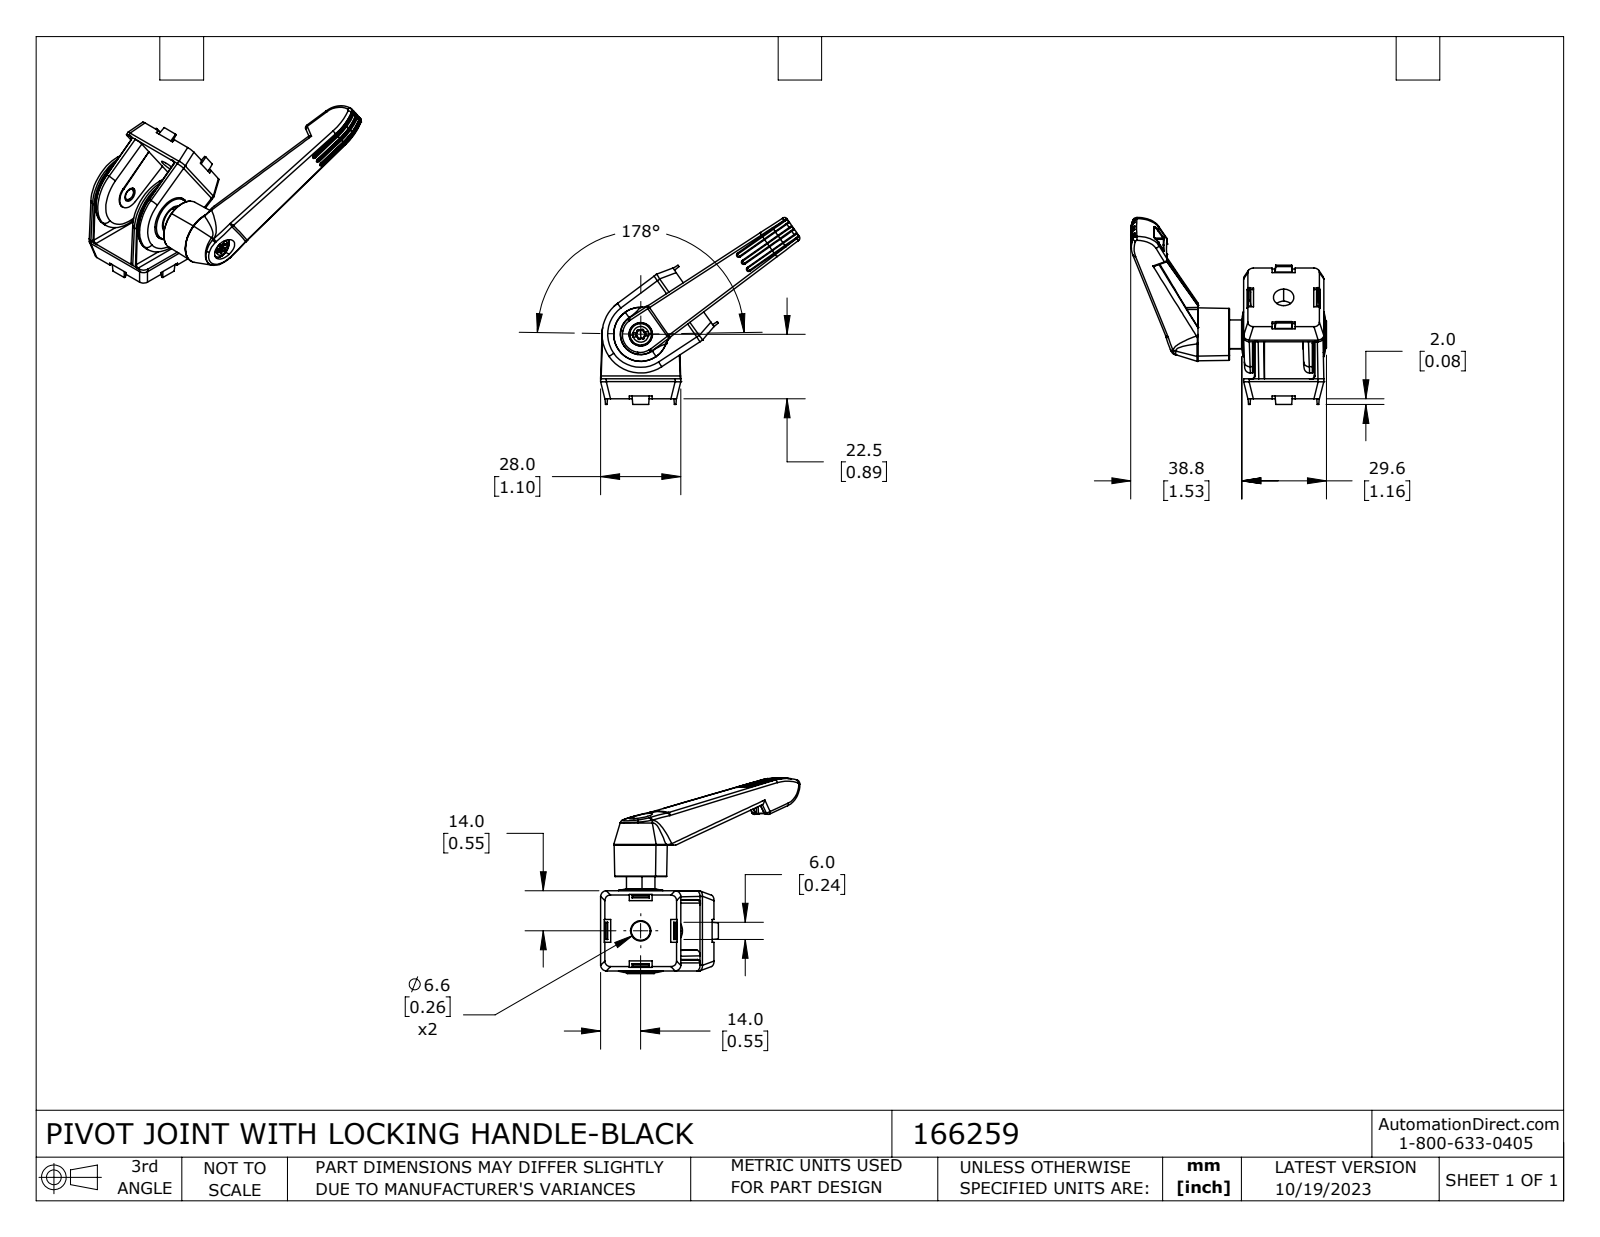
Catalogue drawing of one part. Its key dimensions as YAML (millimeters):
part_name: "166259"
step_written_by: "SolidWorks 2023 (CONFIG_CONTROL_DESIGN)"
units: millimeters
bodies: {solids: 8, faces: 640, planar: 213, cylindrical: 142, other: 285}
overall_size: [69.6, 68.34, 65.31]
volume: 26043
surface_area: 19027
round_holes:
  - {diameter: 2.5, count: 4}
  - {diameter: 4.2, count: 1}
  - {diameter: 5.2, count: 1}
  - {diameter: 7.5, count: 1}
  - {diameter: 8.2, count: 1}
  - {diameter: 22, count: 1}
round_bosses_or_shafts:
  - {diameter: 27, count: 1}
  - {diameter: 15.5, count: 1}
  - {diameter: 14, count: 1}
  - {diameter: 11.2, count: 1}
  - {diameter: 10, count: 1}
  - {diameter: 9.4, count: 1}
  - {diameter: 9, count: 1}
  - {diameter: 8, count: 1}
partial_cylinders:
  - {radius: 2, count: 24}
  - {radius: 0.5, count: 13}
  - {radius: 0.2, count: 10}
  - {radius: 0.4, count: 6}
  - {radius: 0.3, count: 4}
  - {radius: 1, count: 4}
  - {radius: 0.1, count: 3}
face_to_face_distances: [0.5, 7, 20.9, 20.4, 21.4, 1, 3, 16.9, 17.4, 22.7]
hole_center_spacings: [9, 8.31, 15.96, 17.99, 18]
